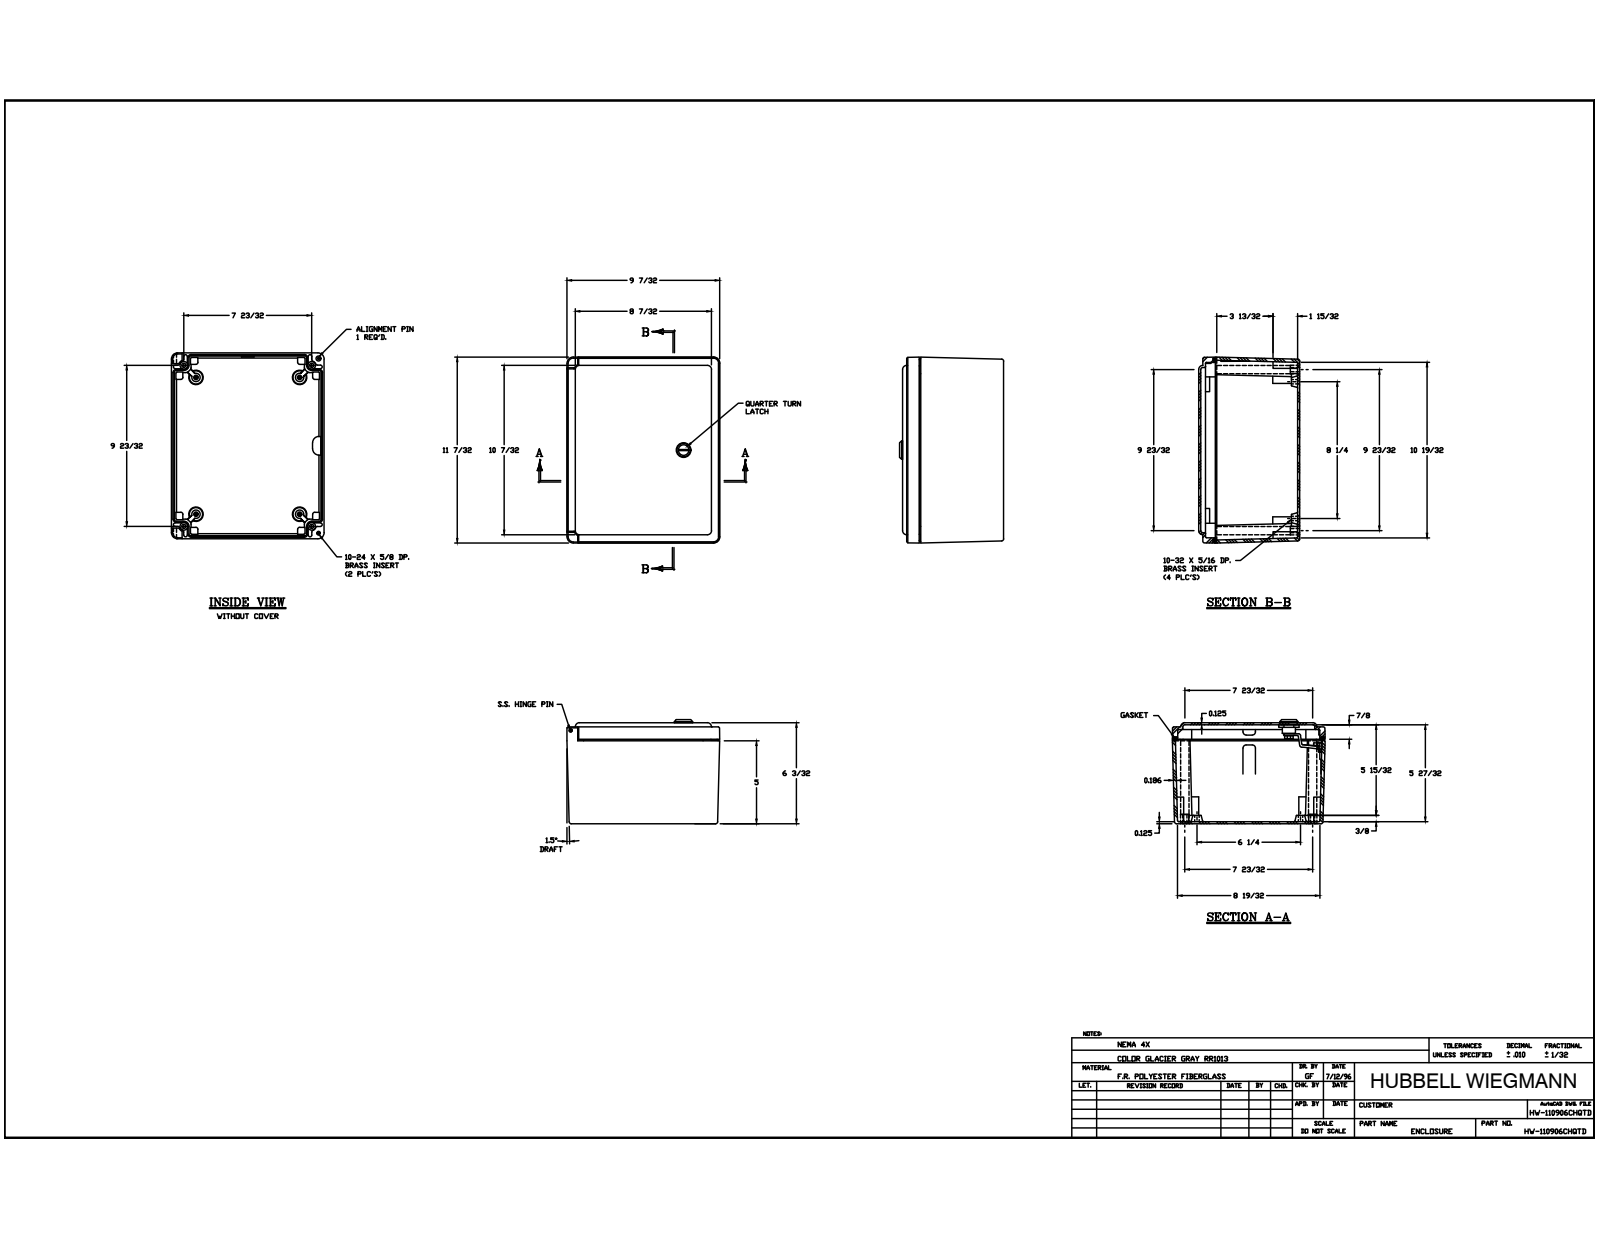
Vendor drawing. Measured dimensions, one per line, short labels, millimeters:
name: WP1109HLBOX; 0.3125-18 X 0.563 DP BRASS INSERT; 10-32 X0.3125 DP BRASS INSERT; 10-24 X 0.625 DP BRASS INSERT (+8 more)
written by: Autodesk Inventor 2014 (AUTOMOTIVE_DESIGN)
unit: mm
bodies: 28 solids, 1095 faces (446 planar, 333 cylindrical, 316 other)
size: 285.26 × 234.52 × 159.54
volume: 1 380 000 mm³; area: 633 194 mm²
holes: 6× ⌀7.14, 4× ⌀3.96, 4× ⌀7.94, 4× ⌀13.49, 2× ⌀2.44, 2× ⌀2.64, 2× ⌀3.3, 2× ⌀3.56, 2× ⌀3.68, 2× ⌀3.97, 2× ⌀4.55, 2× ⌀5.56
bosses: 2× ⌀9.52, 2× ⌀9.42, 2× ⌀5.94, 2× ⌀2.42, 1× ⌀27.78, 1× ⌀16, 1× ⌀10.16, 1× ⌀9.31
rounds: 60× R0.79, 38× R3.17, 30× R1.59, 11× R7.94, 8× R1.5, 8× R4.78, 8× R6.35, 8× R9.53
face distances: 3.17, 151.61, 4.72, 154.78, 148.44, 3.18, 6.35, 148.43, 145.26, 19.05
hole spacings: 26.39, 178.68, 229.26, 289.46, 0.34, 13.42, 14.26, 14.58
